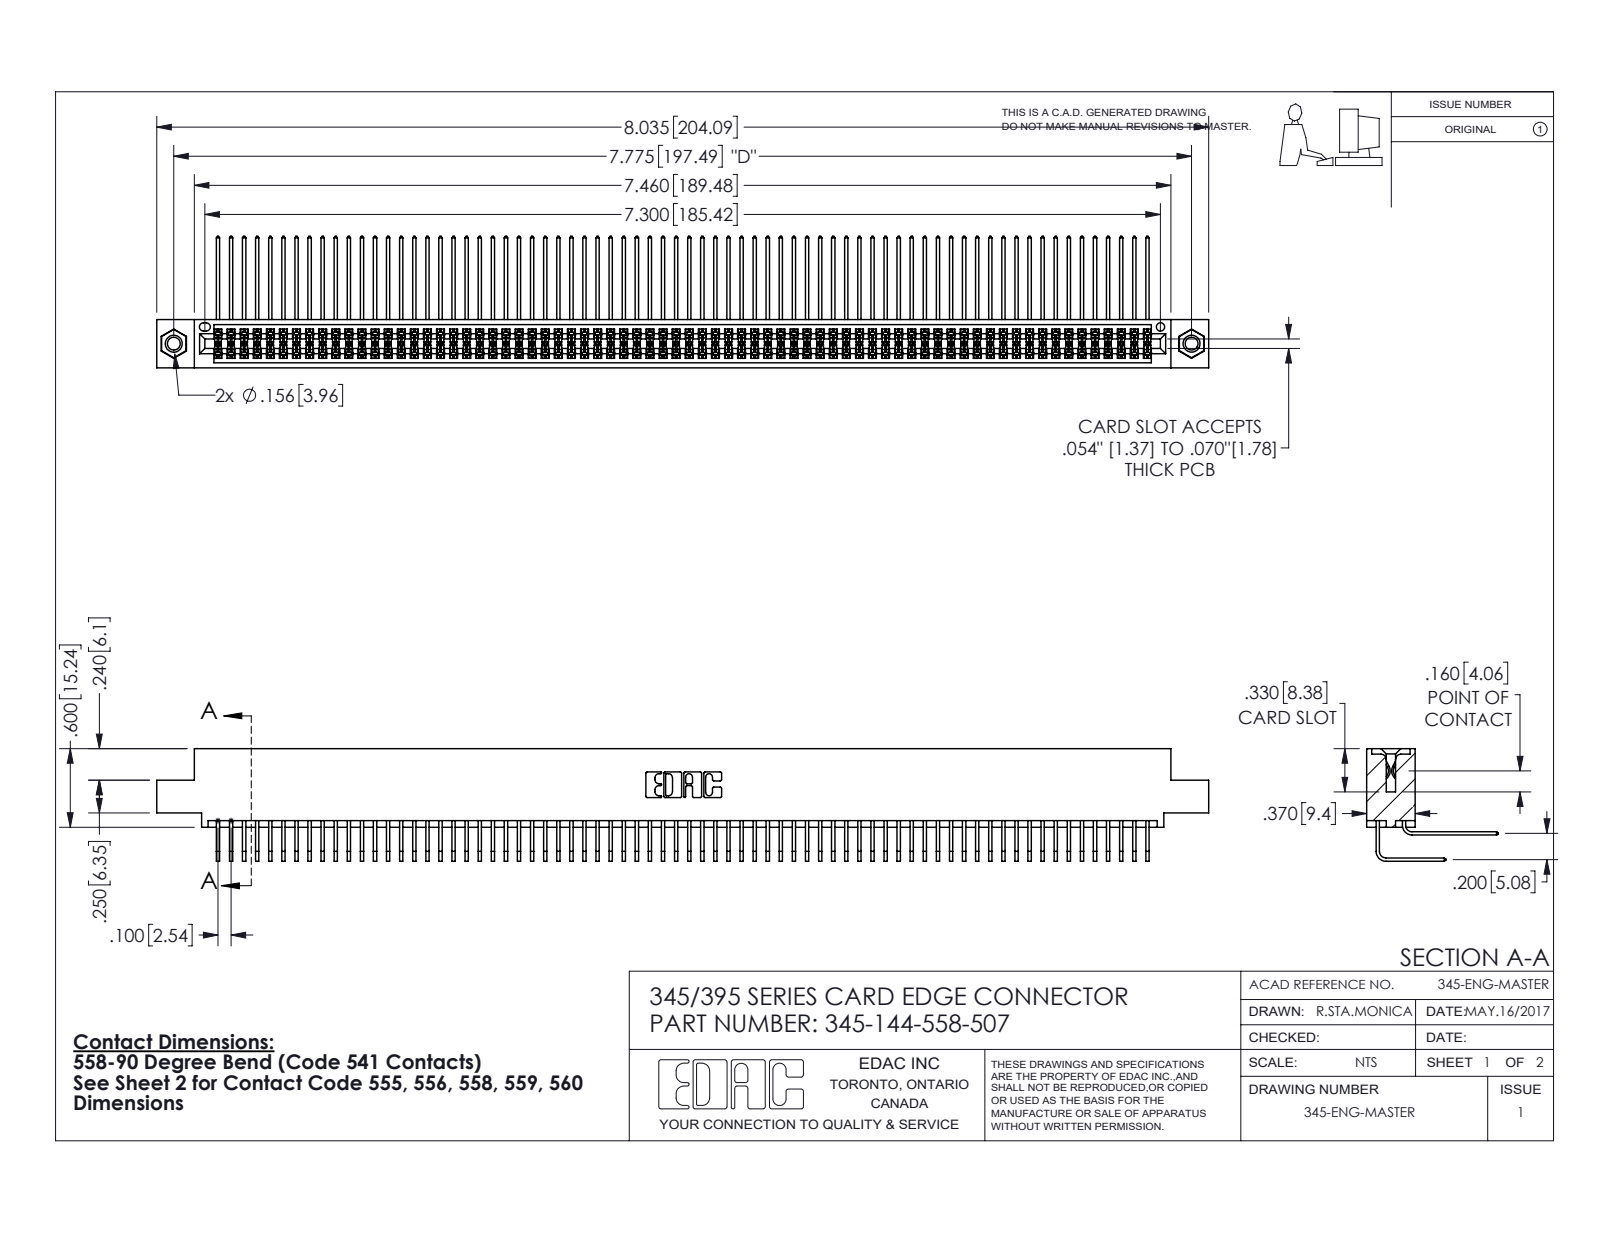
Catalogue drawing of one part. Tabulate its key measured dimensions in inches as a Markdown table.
| quantity | value |
| --- | --- |
| part name | 345-292-001_558 Tail - 2; 345 Part_0.110 Offset - 0.156 Dia-TI; 345-144-558-507; 345-292-001_558 559 Tail - 1 (+1 more) |
| STEP written by | SolidWorks 2016 (CONFIG_CONTROL_DESIGN) |
| units | inches |
| bodies | 147 solids, 7678 faces (5156 planar, 2506 cylindrical, 16 other) |
| overall size | 8.035 × 1.005 × 0.859 |
| volume | 1.272 in³ |
| surface area | 54.91 in² |
| round holes (diameter × count) | 0.098 × 2, 0.125 × 2, 0.156 × 2, 0.064 × 1 |
| round bosses / shafts (diameter × count) | 0.155 × 2 |
| partial cylindrical surfaces (radius × count) | 0.006 × 288, 0.01 × 22, 0.007 × 6, 0.031 × 6, 0.026 × 3, 0.014 × 2, 0.019 × 2, 0.022 × 2 |
| main face-to-face distances | 0.072, 0.298, 0.2, 0.37, 0.098, 0.272, 0.025, 0.225, 0.025, 0.175 |
| hole center spacings | 0.27, 7.539, 7.775 |
